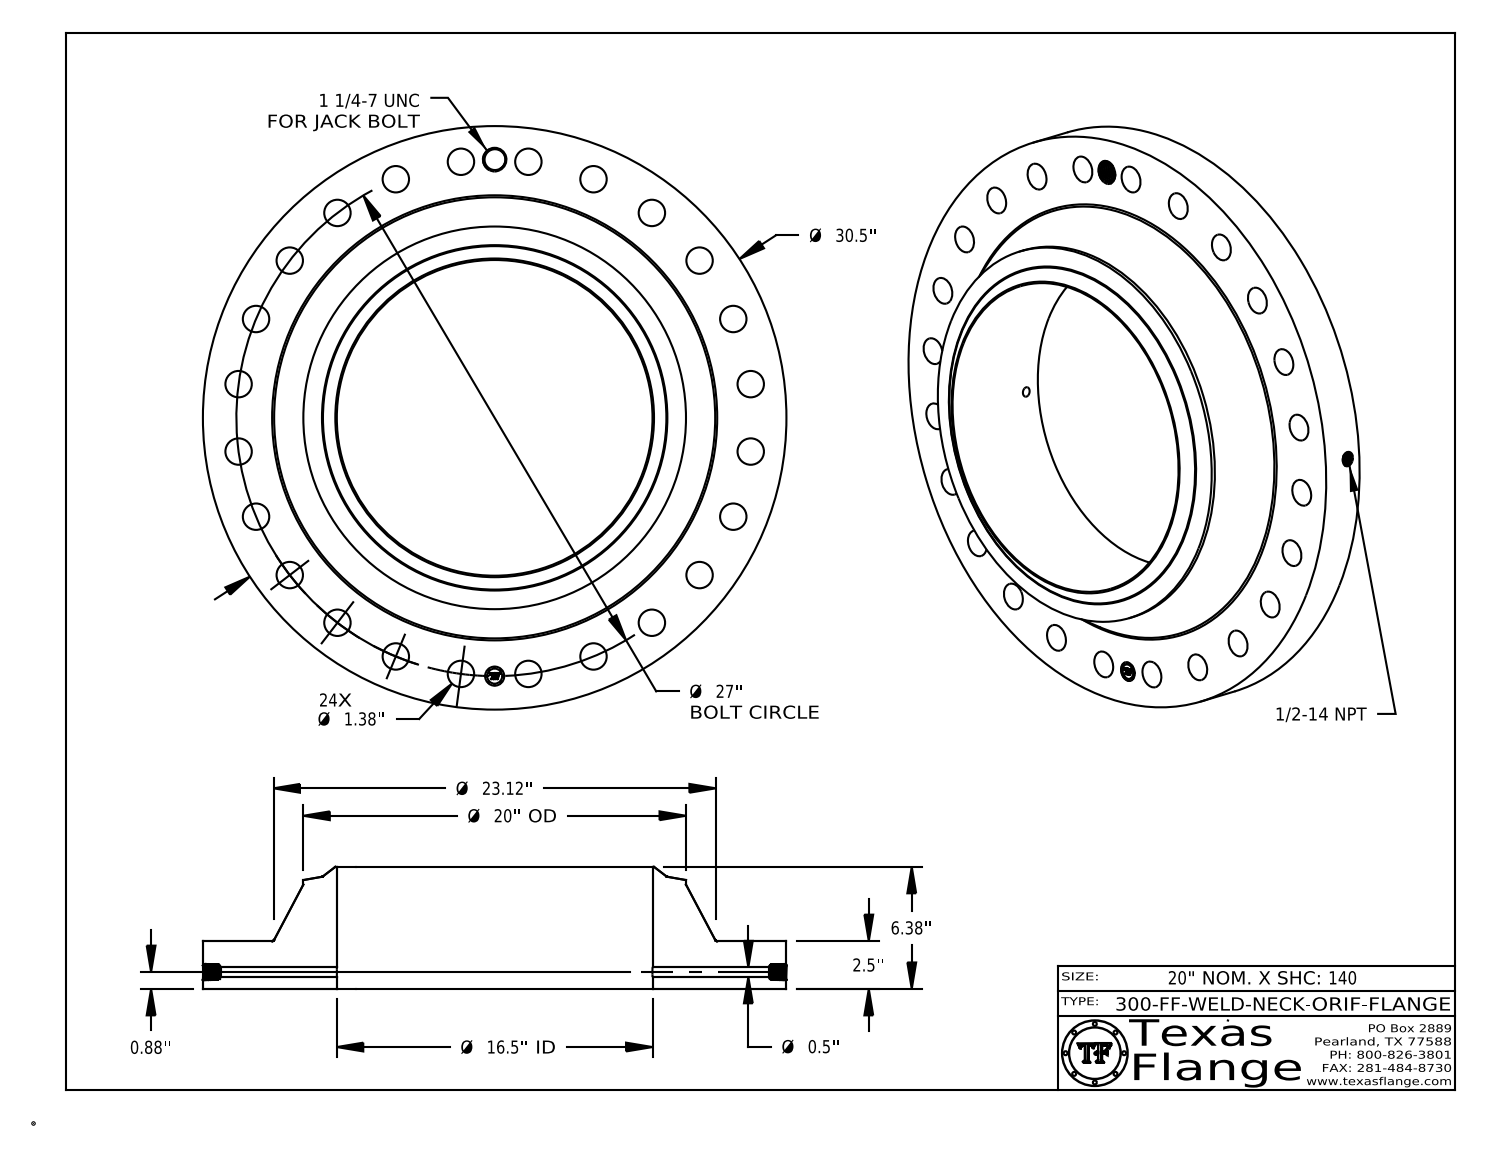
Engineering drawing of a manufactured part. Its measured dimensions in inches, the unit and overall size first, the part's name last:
Units: inches
Overall size (bounding box): 30.5 × 30.5 × 6.38
Round holes (diameter × count): ⌀1.38 ×24, ⌀0.5 ×1, ⌀0.672 ×1, ⌀1 ×1, ⌀1.109 ×1, ⌀16.5 ×1
Round bosses / shafts (diameter × count): ⌀0.061 ×8, ⌀30.5 ×1, ⌀20 ×1, ⌀0.788 ×1
Main face-to-face distances: 2.5, 6.38, 3.88, 2.485, 0.015, 3.895, 0.298, 0.293, 0.054, 0.248
Hole centre spacings: 13.5, 23.383, 24.945, 21.42, 3.524, 6.988, 19.092, 26.08
Volume: 1 692 in³ · Surface area: 1 973 in²
Bodies: 1 solid, 819 faces (368 planar, 129 cylindrical, 322 other)
Part name (STEP PRODUCT): 300-FF-WELD-NECK
STEP written by: CATIA V5 STEP AP214 (AUTOMOTIVE_DESIGN)
